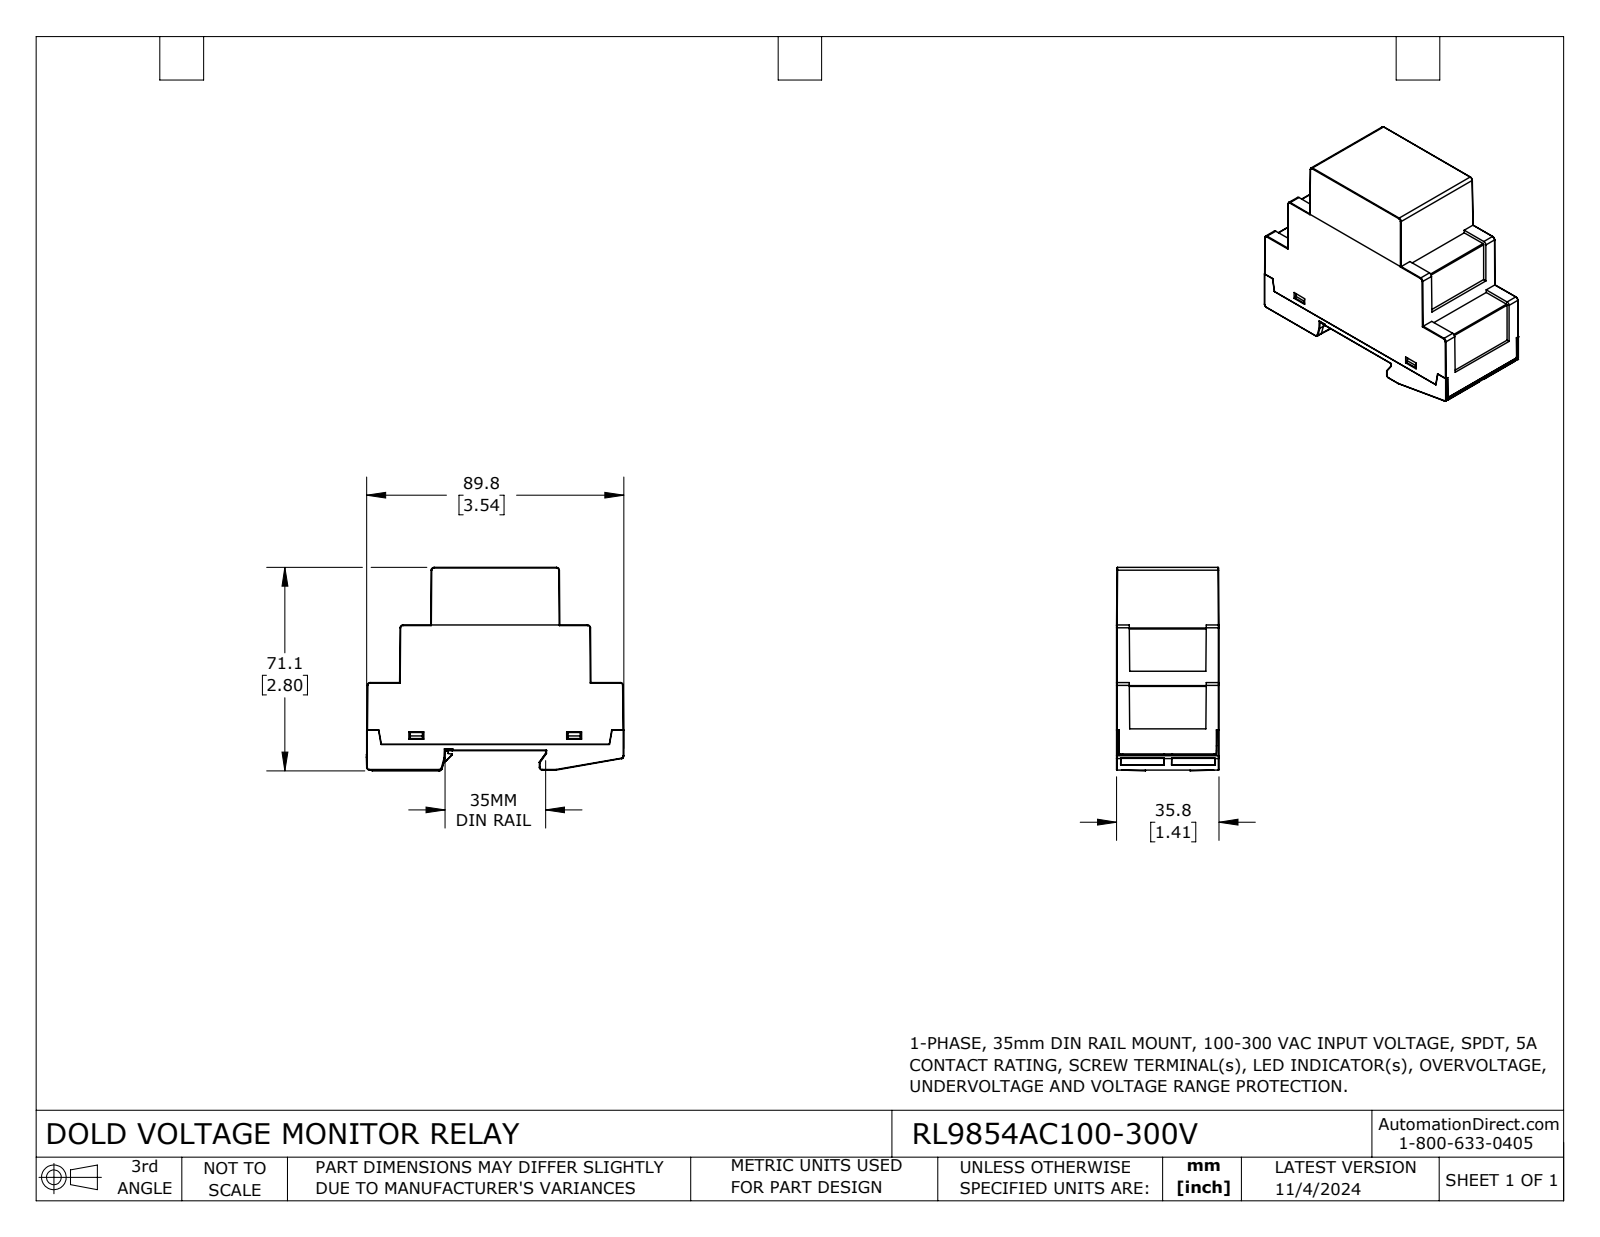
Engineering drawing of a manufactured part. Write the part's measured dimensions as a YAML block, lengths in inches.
part_name: "RL9854AC100-300V"
step_written_by: "SolidWorks 2023 (CONFIG_CONTROL_DESIGN)"
units: inches
bodies: {solids: 2, faces: 643, planar: 492, cylindrical: 113, other: 38}
overall_size: [3.538, 2.799, 1.409]
volume: 9.342
surface_area: 55.38
round_bosses_or_shafts:
  - {diameter: 0.098, count: 2}
  - {diameter: 0.315, count: 1}
partial_cylinders:
  - {radius: 0.008, count: 42}
  - {radius: 0.039, count: 14}
  - {radius: 0.02, count: 11}
  - {radius: 0.004, count: 6}
  - {radius: 0.012, count: 4}
  - {radius: 0.079, count: 4}
  - {radius: 0.011, count: 1}
  - {radius: 0.016, count: 1}
face_to_face_distances: [1.409, 0.217, 2.52, 0.035, 0.085, 2.435, 2.219, 0.301, 0.824, 1.374]
